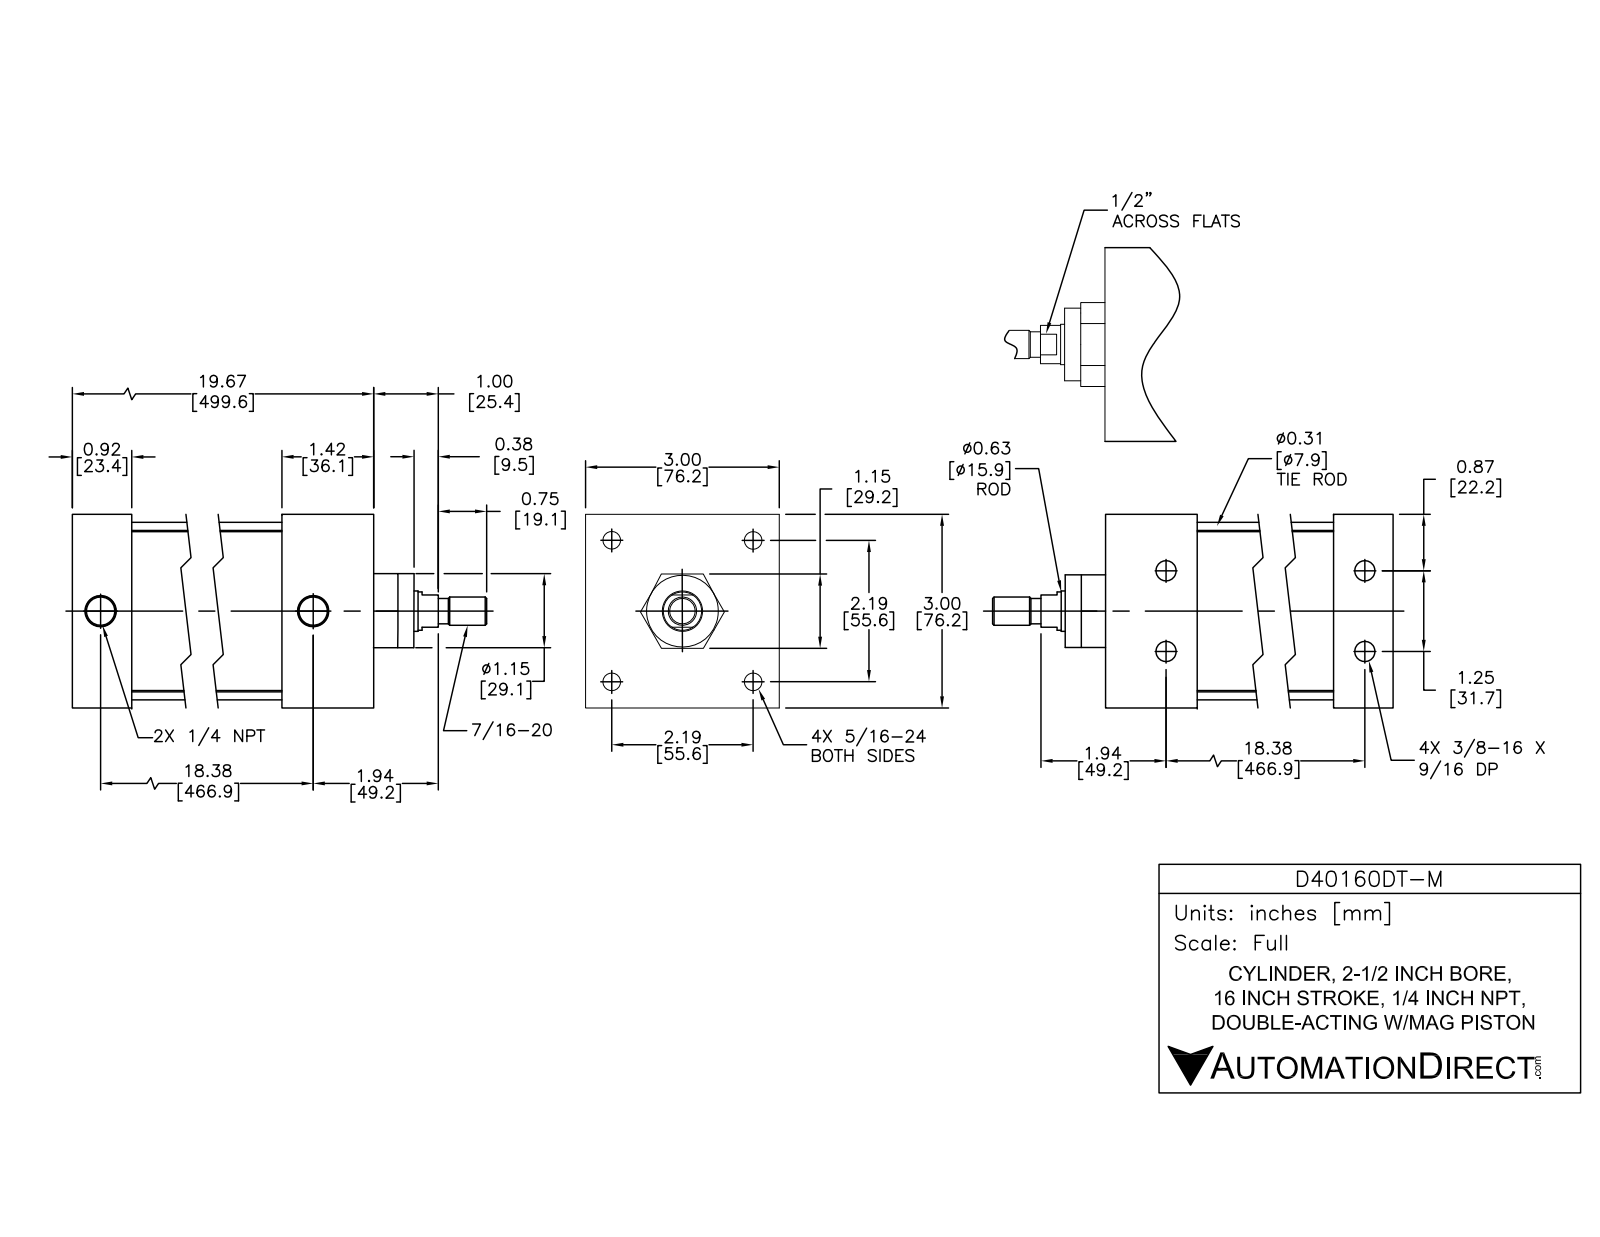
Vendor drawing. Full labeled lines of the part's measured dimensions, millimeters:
Part name (STEP PRODUCT): D40160DT-M; D40160DT-M PISTON; D40160DT-M BODY
STEP written by: SolidWorks 2015 (AUTOMOTIVE_DESIGN)
Units: millimetres
Bodies: 12 solids, 298 faces (94 planar, 114 cylindrical, 90 other)
Overall size (bounding box): 546 × 76.2 × 76.2
Volume: 894 100 mm³ · Surface area: 325 500 mm²
Round holes (diameter × count): ⌀6.8 ×4, ⌀7.8 ×4, ⌀9.1 ×4, ⌀12.7 ×4, ⌀7.5 ×2, ⌀12.1 ×2, ⌀15.9 ×1, ⌀16 ×1, ⌀63.5 ×1
Round bosses / shafts (diameter × count): ⌀12.3 ×4, ⌀8 ×4, ⌀7.2 ×4, ⌀69.9 ×1, ⌀63.4 ×1, ⌀28.4 ×1, ⌀15.8 ×1, ⌀15 ×1
Partial cylindrical surfaces — rounded edges, fillets, slot ends (radius × count): R7.6 ×4
Main face-to-face distances: 76.2, 501.5, 475.6, 25.9, 36.1, 439.6, 465.5, 25.4, 478.2, 442.1
Hole centre spacings: 39.5, 55.9, 466.9, 466.6, 15.9, 15.9, 31.8, 79
